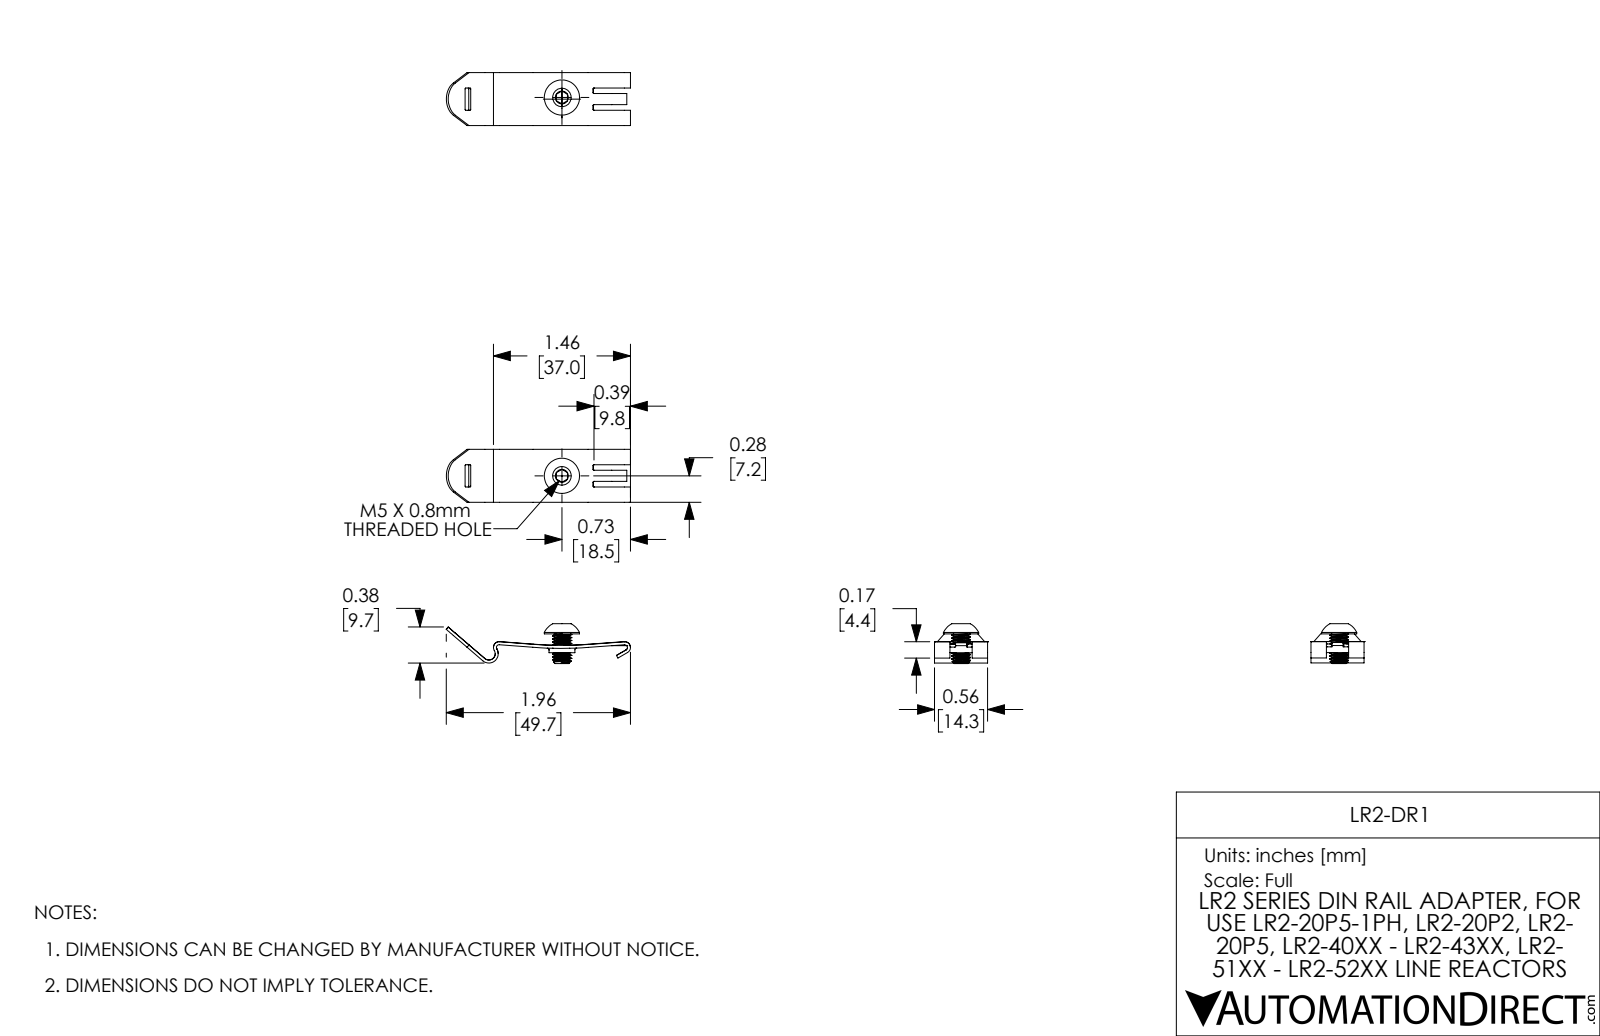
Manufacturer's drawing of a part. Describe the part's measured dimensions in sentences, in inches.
The part is named "L2R-DR1". Its 3-D file was written by "SolidWorks 2017 (AUTOMOTIVE_DESIGN)". It is 4 solids with 282 faces: 80 planar, 166 cylindrical and 36 other. Overall it measures 4.563 by 1.956 by 0.423 inches. Its volume is 0.108 cubic inches and its surface area 6.599 square inches. Round holes: 2 of diameter 0.163, 1 of diameter 0.197. Round bosses or shafts: 2 of diameter 0.374, 2 of diameter 0.276, 2 of diameter 0.197, 2 of diameter 0.156. Partial cylindrical surfaces (rounded edges, fillets, slot ends): 20 of radius 0.01, 4 of radius 0.03, 4 of radius 0.061, 2 of radius 0.067, 2 of radius 0.099, 2 of radius 0.197, 2 of radius 3.937, 2 of radius 3.969. The main face-to-face distances are 0.031, 0.033, 0.03, 0.03, 0.033, 4, 0.563, 0.4, 0.163, 4.563. The hole center spacings are 4.
